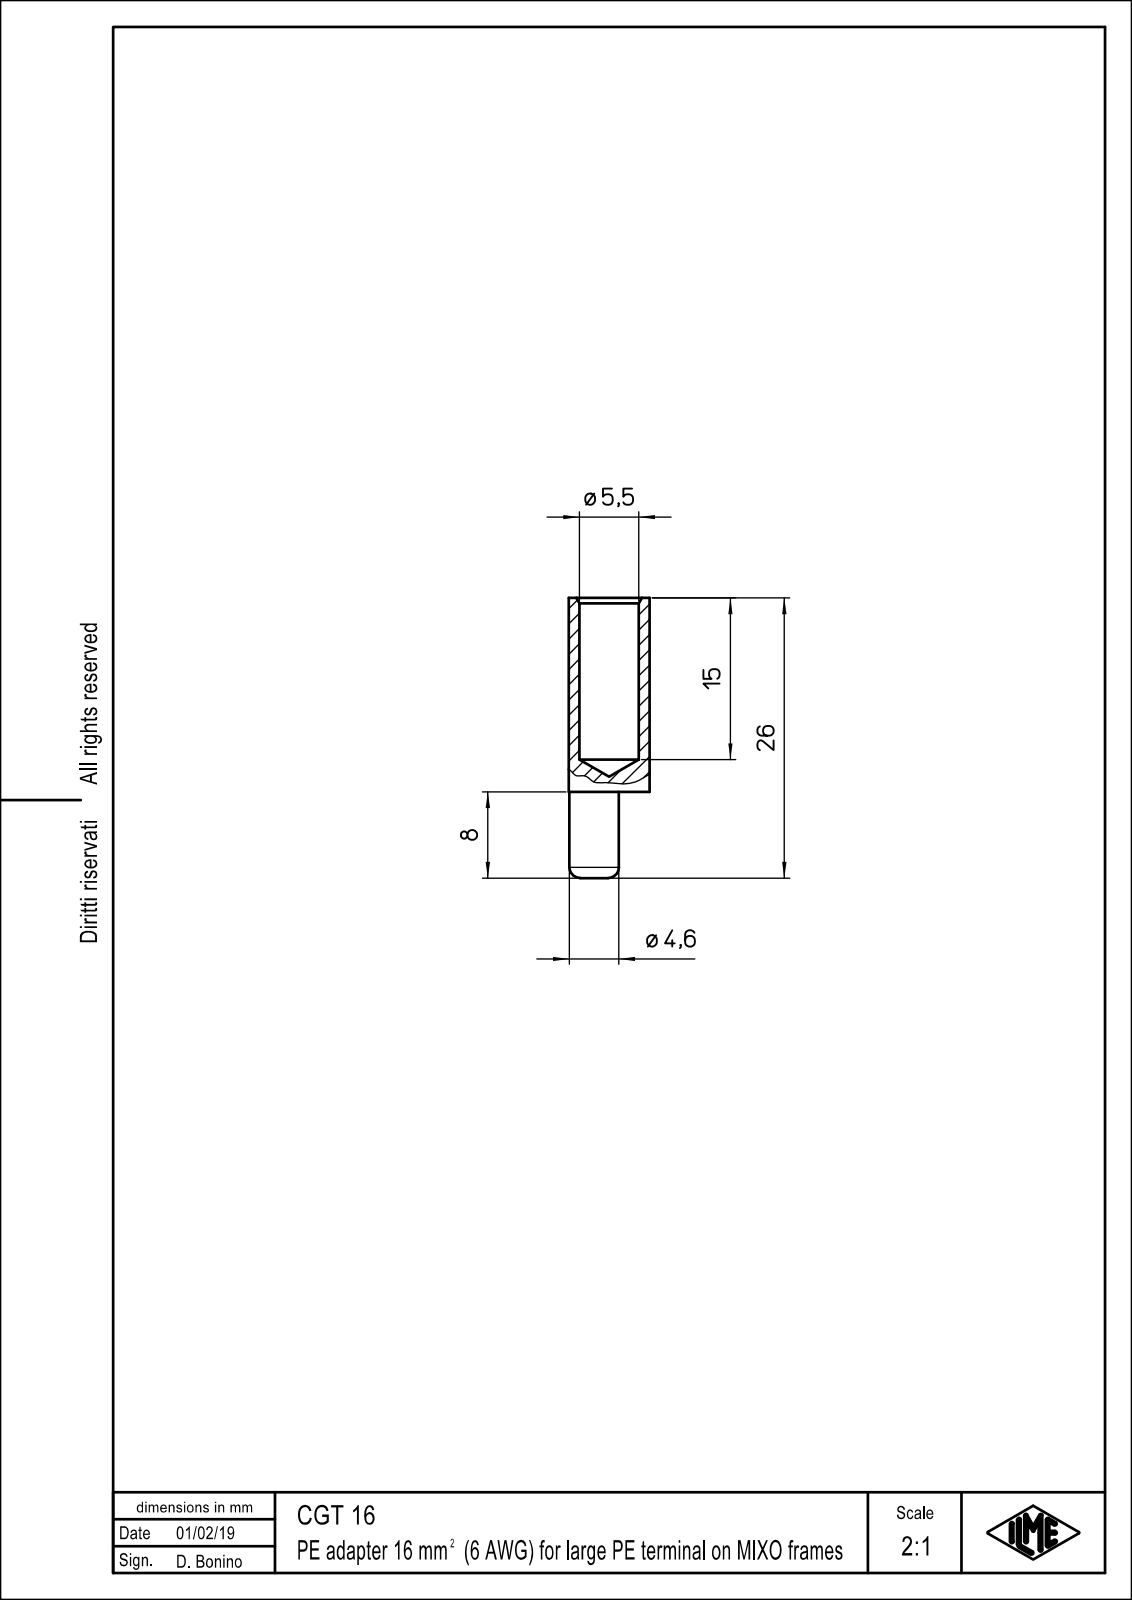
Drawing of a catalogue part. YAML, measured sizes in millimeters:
part_name: "CGT_16"
step_written_by: "PTC Creo Elements/Direct Modeling 19.0B 21-Mar-2015 (C) Parametric Technology GmbH (AUTOMOTIVE_DESIGN)"
units: millimeters
bodies: {solids: 1, faces: 15, planar: 3, cylindrical: 6, other: 6}
overall_size: [26, 7.5, 7.5]
volume: 555
surface_area: 881
round_holes:
  - {diameter: 5.5, count: 1}
round_bosses_or_shafts:
  - {diameter: 7.5, count: 1}
  - {diameter: 4.6, count: 1}
face_to_face_distances: [18, 26, 8]
